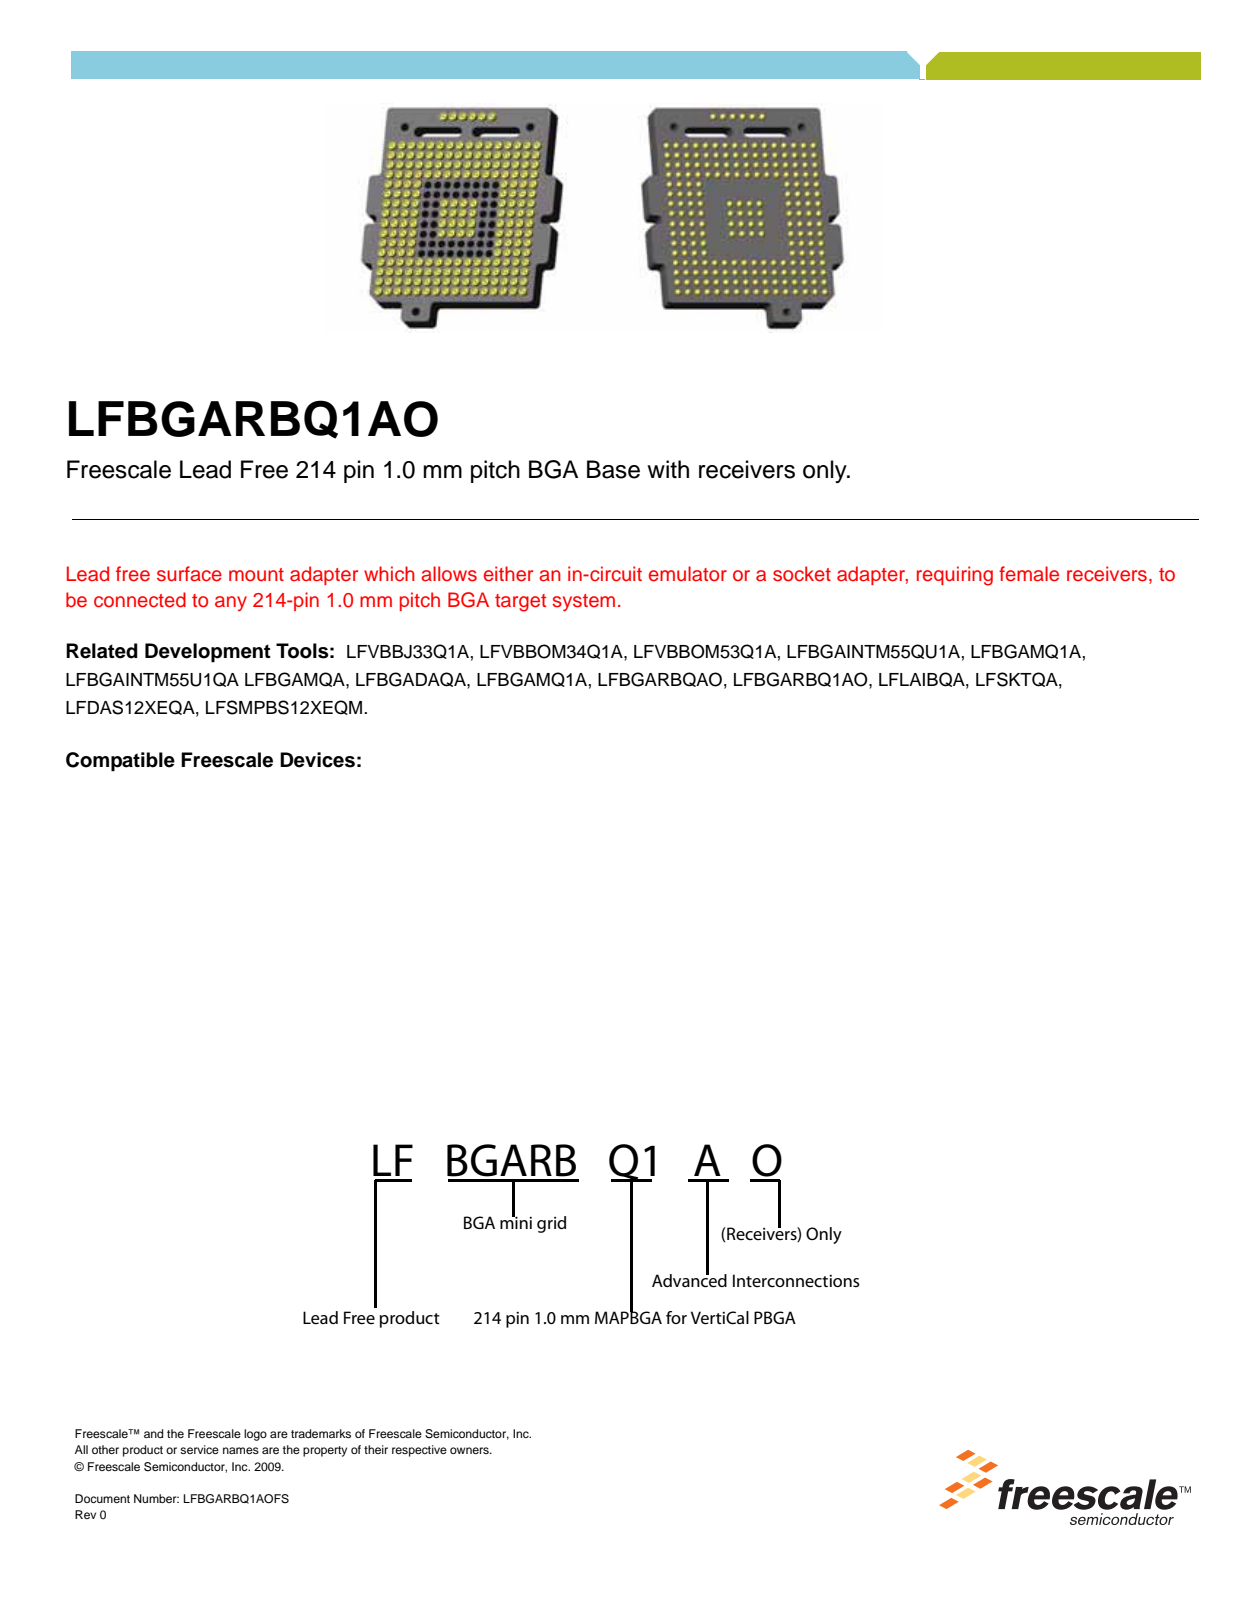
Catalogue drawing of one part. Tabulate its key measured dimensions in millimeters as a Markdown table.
| quantity | value |
| --- | --- |
| STEP written by | Mechanical Desktop 2011 (CONFIG_CONTROL_DESIGN) |
| units | millimeters |
| bodies | 215 solids, 3830 faces (1141 planar, 2261 cylindrical, 428 other) |
| overall size | 22 × 19.38 × 3.22 |
| volume | 785 mm³ |
| surface area | 3 925 mm² |
| round holes (diameter × count) | 0.75 × 262, 0.58 × 214, 0.84 × 3 |
| round bosses / shafts (diameter × count) | 0.38 × 214 |
| partial cylindrical surfaces (radius × count) | 0.38 × 15, 0.5 × 4 |
| main face-to-face distances | 2.24, 1.94, 0.67, 0.37, 1.57, 2.47, 2.17, 1.8, 2.67, 2.37 |
| hole center spacings | 1, 2, 2.24, 1.41, 3, 3.16, 3.61, 6.4 |
